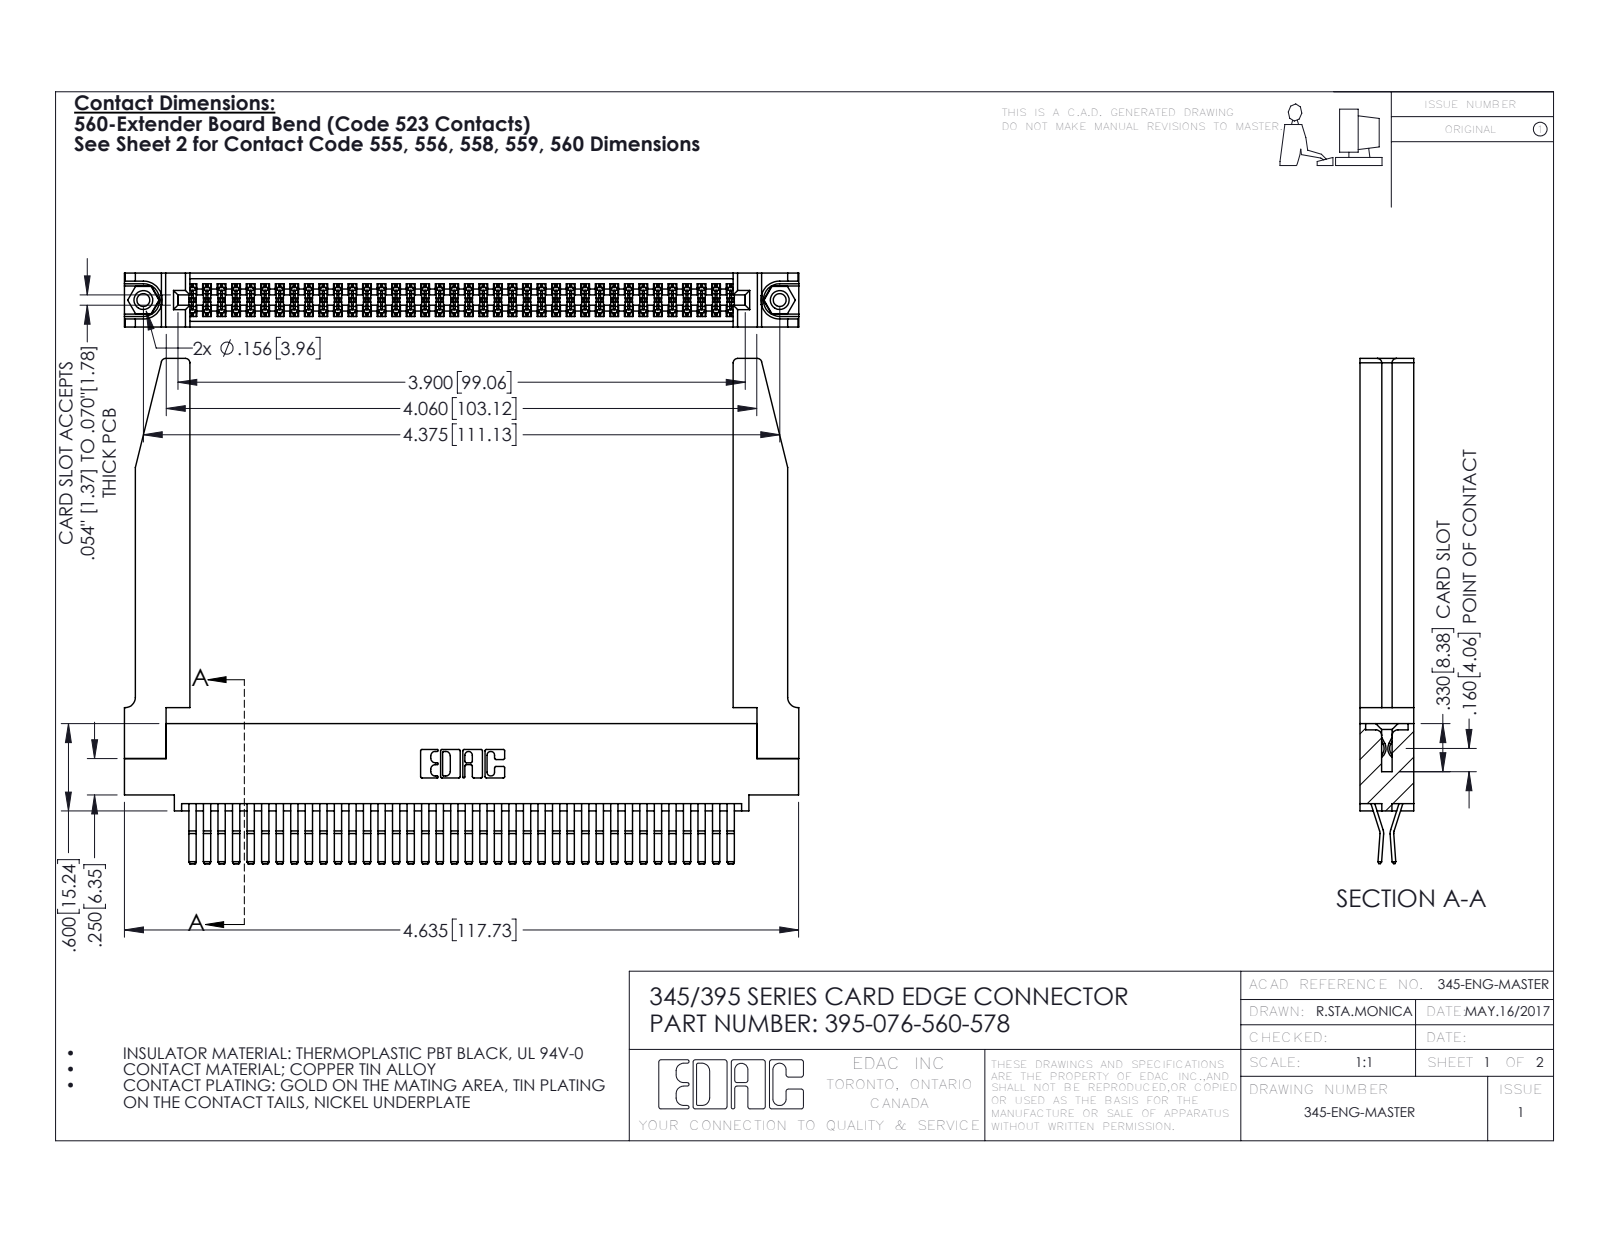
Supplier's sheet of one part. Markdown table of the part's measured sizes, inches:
| quantity | value |
| --- | --- |
| part name | 345-220-078_345-220-078; 345 Part_0.110 Offset - 0.156 Dia-TH; 345-250-001_345-250-001-102; 395-076-560-578 (+1 more) |
| STEP written by | SolidWorks 2016 (CONFIG_CONTROL_DESIGN) |
| units | inches |
| bodies | 81 solids, 4316 faces (2734 planar, 1530 cylindrical, 52 other) |
| overall size | 4.636 × 3.472 × 0.37 |
| volume | 1.196 in³ |
| surface area | 39.71 in² |
| round holes (diameter × count) | 0.089 × 2, 0.125 × 2, 0.156 × 2, 0.064 × 1 |
| round bosses / shafts (diameter × count) | 0.155 × 2 |
| partial cylindrical surfaces (radius × count) | 0.006 × 114, 0.01 × 22, 0.03 × 8, 0.007 × 6, 0.031 × 6, 0.026 × 3, 0.01 × 2, 0.014 × 2 |
| main face-to-face distances | 0.37, 0.072, 0.298, 0.025, 0.2, 0.098, 0.272, 0.225, 0.148, 0.15 |
| hole center spacings | 0.27, 4.139, 4.375 |
